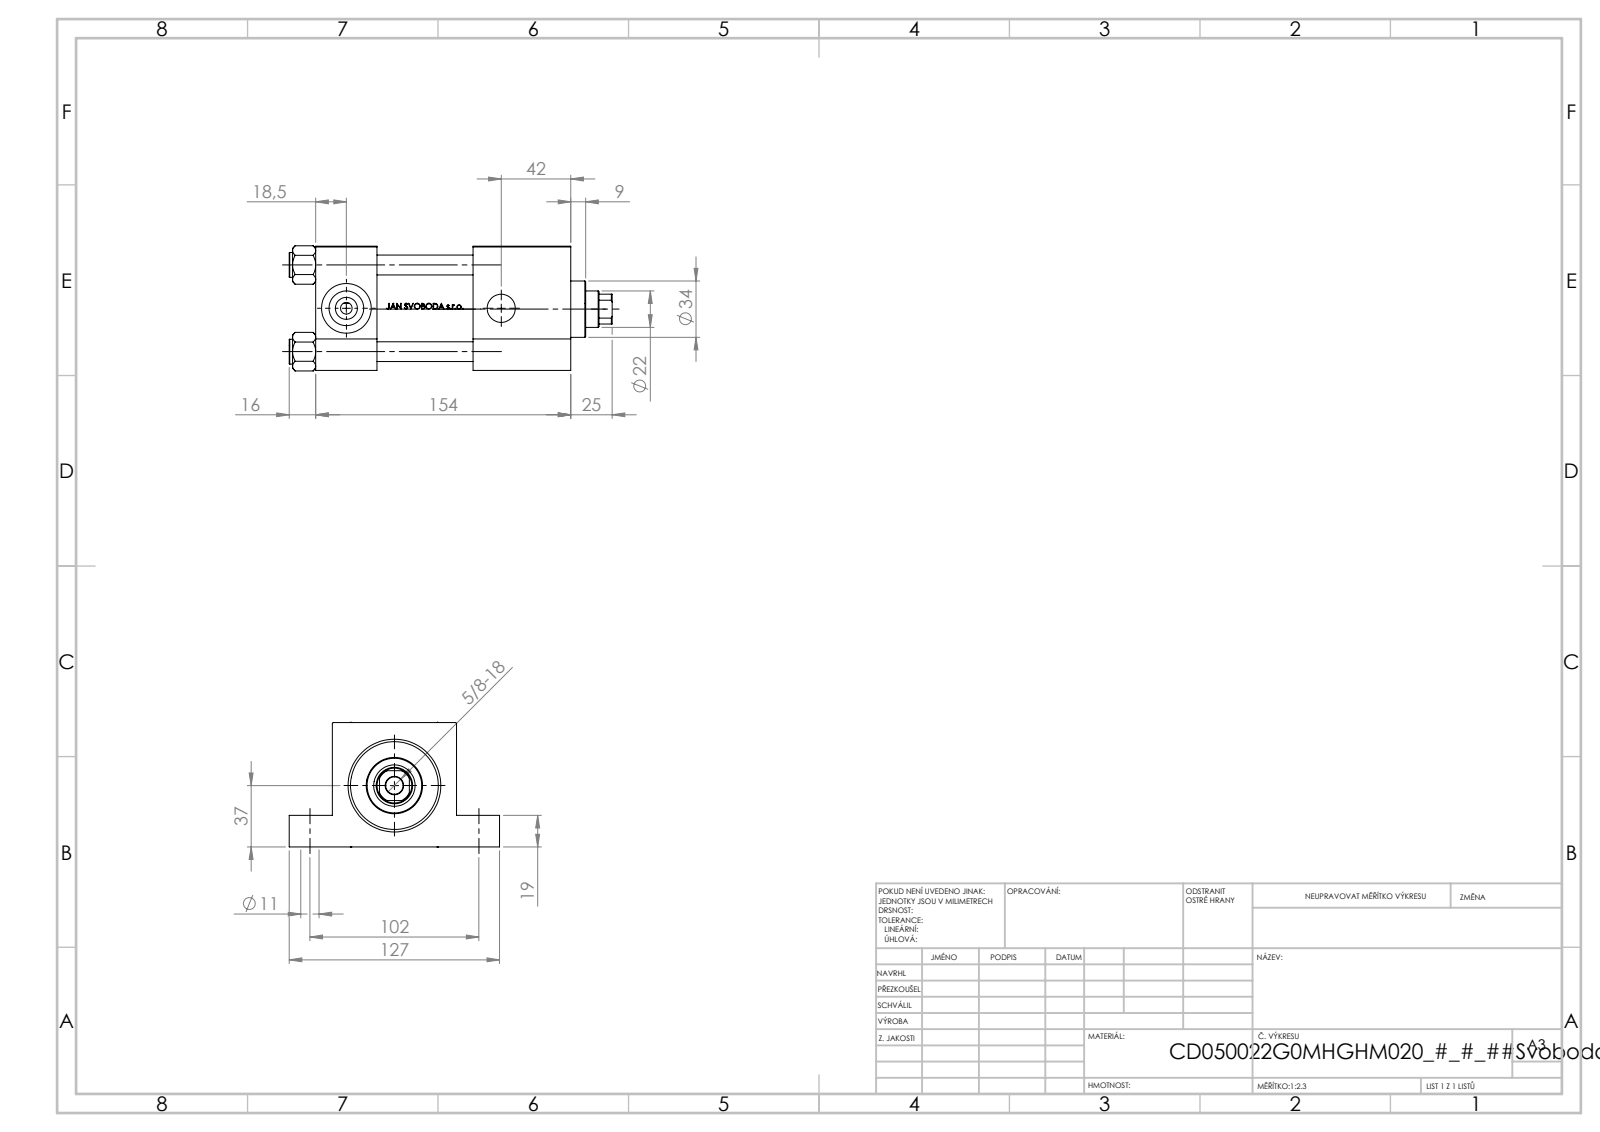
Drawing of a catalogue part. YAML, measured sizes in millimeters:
part_name: "V215CD_G_TYCINKA; V215CD_VC_G; V215CD_VCP_G; V215CD_G_Body (+1 more)"
step_written_by: "SolidWorks 2019 (CONFIG_CONTROL_DESIGN)"
units: millimeters
bodies: {solids: 11, faces: 1087, planar: 431, cylindrical: 124, other: 532}
overall_size: [195, 127, 75.54]
volume: 755944
surface_area: 159552
round_holes:
  - {diameter: 11, count: 4}
  - {diameter: 12, count: 4}
  - {diameter: 7, count: 2}
  - {diameter: 20.96, count: 2}
  - {diameter: 10.5, count: 1}
  - {diameter: 17, count: 1}
  - {diameter: 22, count: 1}
  - {diameter: 25, count: 1}
  - {diameter: 30, count: 1}
  - {diameter: 41, count: 1}
  - {diameter: 50, count: 1}
  - {diameter: 53, count: 1}
round_bosses_or_shafts:
  - {diameter: 15, count: 4}
  - {diameter: 56, count: 1}
  - {diameter: 34, count: 1}
partial_cylinders:
  - {radius: 10.5, count: 1}
face_to_face_distances: [75, 37, 154, 117, 19, 56, 95, 58, 59, 26]
hole_center_spacings: [52.3, 36.63, 37.34, 73.96, 102, 112, 151.49, 93.5]
